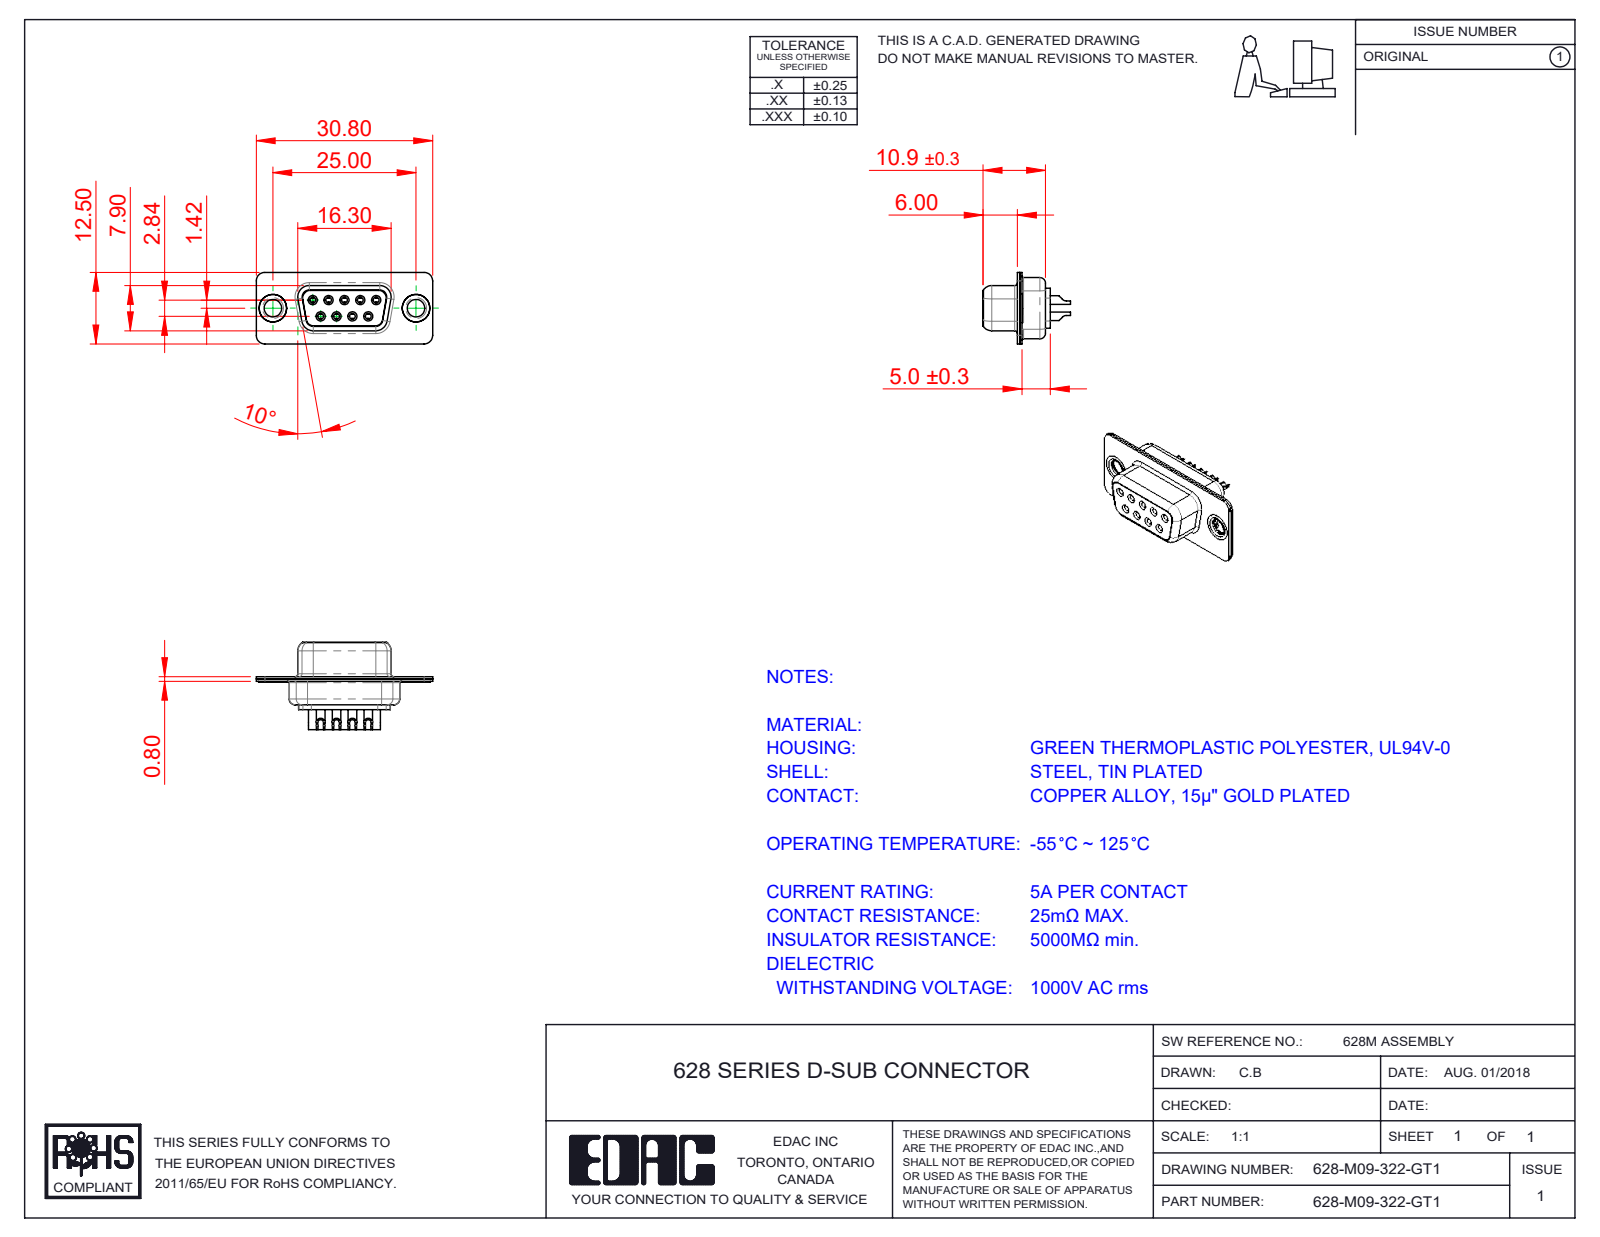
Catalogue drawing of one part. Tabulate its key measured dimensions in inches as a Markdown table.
| quantity | value |
| --- | --- |
| part name | 628M Contact Row 2_22; 628M Housing_09 Contacts; 628M Shell Front_09 Contacts; 628M Shell Rear_09 Contacts (+3 more) |
| STEP written by | SolidWorks 2020 (CONFIG_CONTROL_DESIGN) |
| units | inches |
| bodies | 14 solids, 749 faces (221 planar, 310 cylindrical, 218 other) |
| overall size | 1.213 × 0.6 × 0.492 |
| volume | 0.1 in³ |
| surface area | 6.75 in² |
| round holes (diameter × count) | 0.039 × 9, 0.043 × 9, 0.067 × 9, 0.071 × 9, 0.079 × 9, 0.12 × 2, 0.157 × 2, 0.189 × 2 |
| round bosses / shafts (diameter × count) | 0.087 × 9, 0.063 × 9, 0.059 × 9, 0.197 × 2, 0.193 × 2, 0.14 × 2 |
| partial cylindrical surfaces (radius × count) | 0.059 × 16, 0.079 × 12, 0.053 × 8, 0.063 × 8, 0.039 × 6, 0.01 × 4, 0.02 × 4, 0.024 × 4 |
| main face-to-face distances | 0.016, 0.055, 0.018, 0.333, 0.031, 0.35, 0.071, 0.278, 0.039, 0.033 |
| hole center spacings | 0.124, 0.109, 0.218, 0.198, 0.198, 0.327, 0.28, 0.294 |
